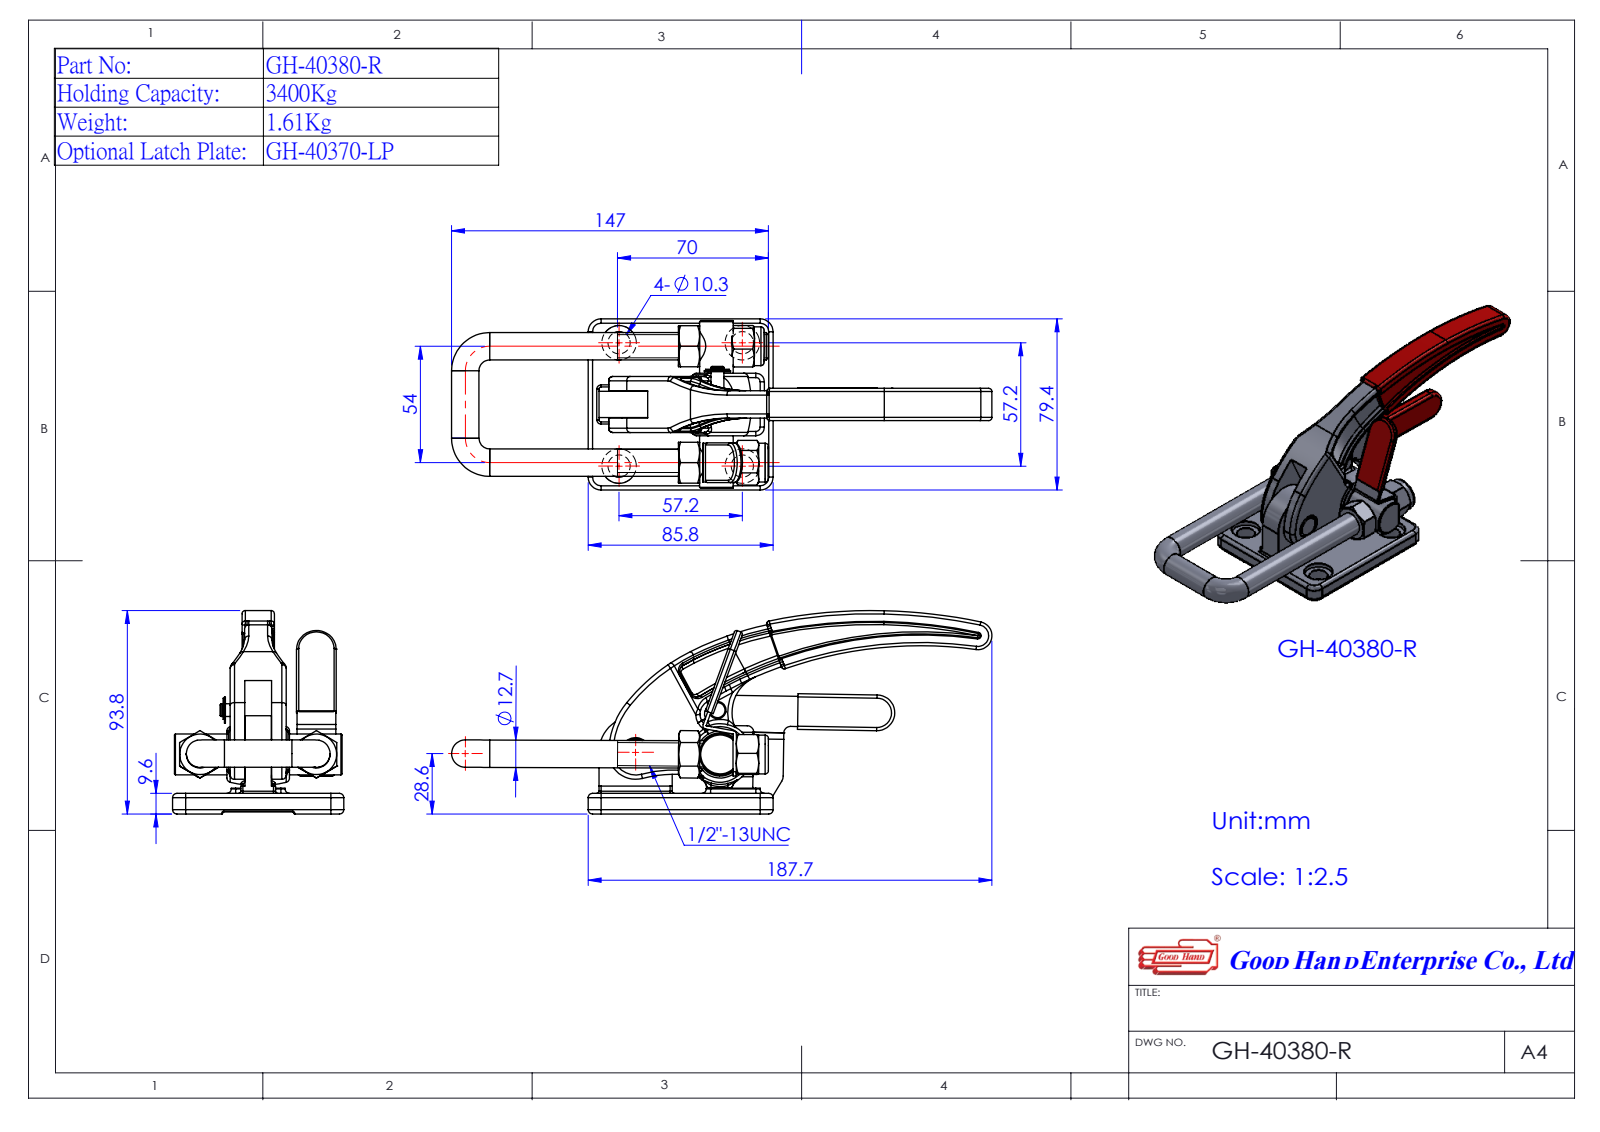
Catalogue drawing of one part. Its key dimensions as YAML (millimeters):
part_name: "Group4^GH-40380-R(簡化); Group1^GH-40380-R(簡化); 340380R13-2^GH-40380-R(簡化); GH-40380-R(簡化) (+1 more)"
step_written_by: "SolidWorks 2016 (AUTOMOTIVE_DESIGN)"
units: millimeters
bodies: {solids: 7, faces: 483, planar: 202, cylindrical: 152, other: 129}
overall_size: [250.6, 94.38, 79.4]
volume: 226108
surface_area: 76663
round_holes:
  - {diameter: 10.3, count: 4}
  - {diameter: 16, count: 4}
  - {diameter: 10.2, count: 2}
  - {diameter: 12, count: 2}
  - {diameter: 12.7, count: 2}
  - {diameter: 13.5, count: 2}
  - {diameter: 13.71, count: 2}
  - {diameter: 9.5, count: 1}
  - {diameter: 12.5, count: 1}
  - {diameter: 19, count: 1}
round_bosses_or_shafts:
  - {diameter: 12.7, count: 3}
  - {diameter: 18, count: 2}
  - {diameter: 8, count: 1}
  - {diameter: 5.95, count: 1}
partial_cylinders:
  - {radius: 2, count: 18}
  - {radius: 6, count: 6}
  - {radius: 1.5, count: 5}
  - {radius: 3, count: 3}
  - {radius: 3.01, count: 2}
  - {radius: 5, count: 2}
  - {radius: 6.47, count: 2}
  - {radius: 65.68, count: 2}
face_to_face_distances: [9.6, 1.5, 1, 6.75, 19.25, 8.6, 20.5, 19, 5.5, 1.25]
hole_center_spacings: [54, 57.2, 80.89, 39.25]
